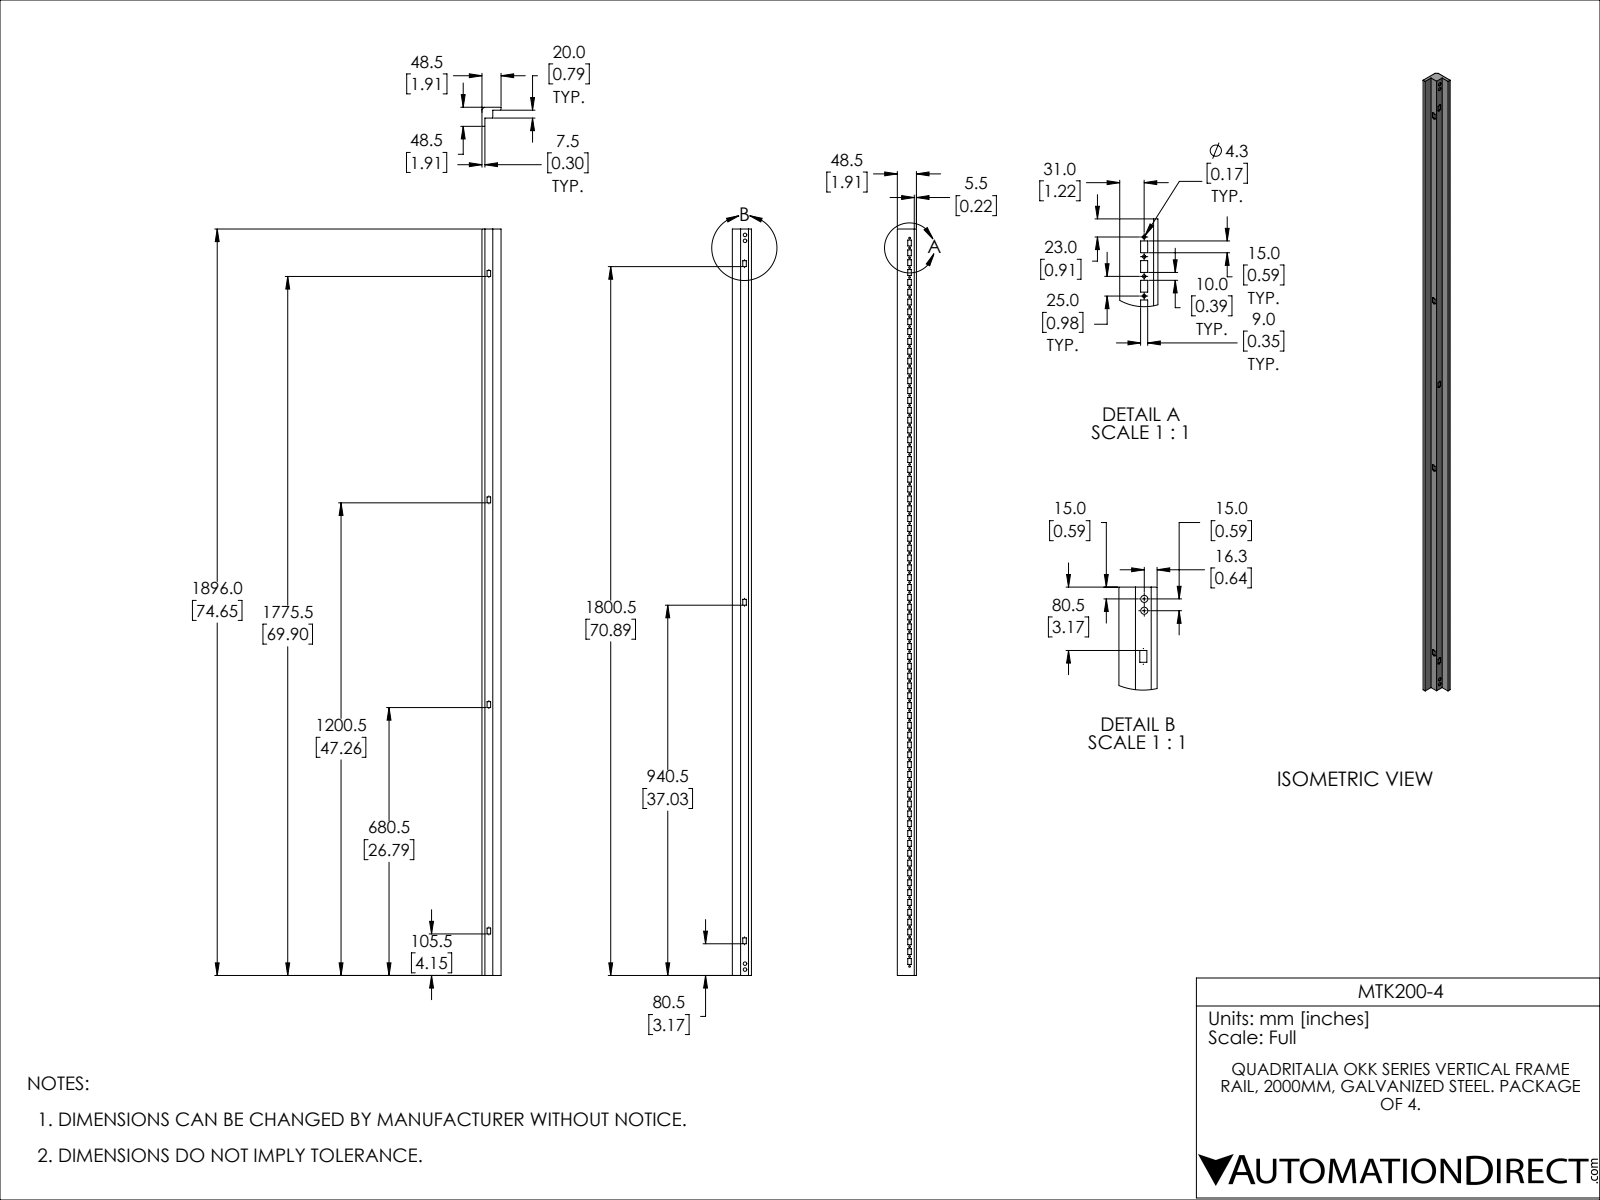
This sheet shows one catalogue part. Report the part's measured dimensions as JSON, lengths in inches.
{"part_name": "MTK200-4", "step_written_by": "SolidWorks 2021 (AUTOMOTIVE_DESIGN)", "units": "inches", "bodies": {"solids": 4, "faces": 4488, "planar": 3816, "cylindrical": 672, "other": 0}, "overall_size": [74.646, 9.409, 1.909], "volume_in3": 482, "surface_area_in2": 2327, "round_holes": [[0.167, 375], [0.01, 38], [0.354, 4]], "face_to_face_distances": [2.5, 5, 0.295, 1.083, 0.787, 7.5, 2.795, 2.205, 1.909, 1.614], "hole_center_spacings": [0.984, 1.969, 2.953, 3.937, 4.921, 5.906, 6.89, 7.874]}
